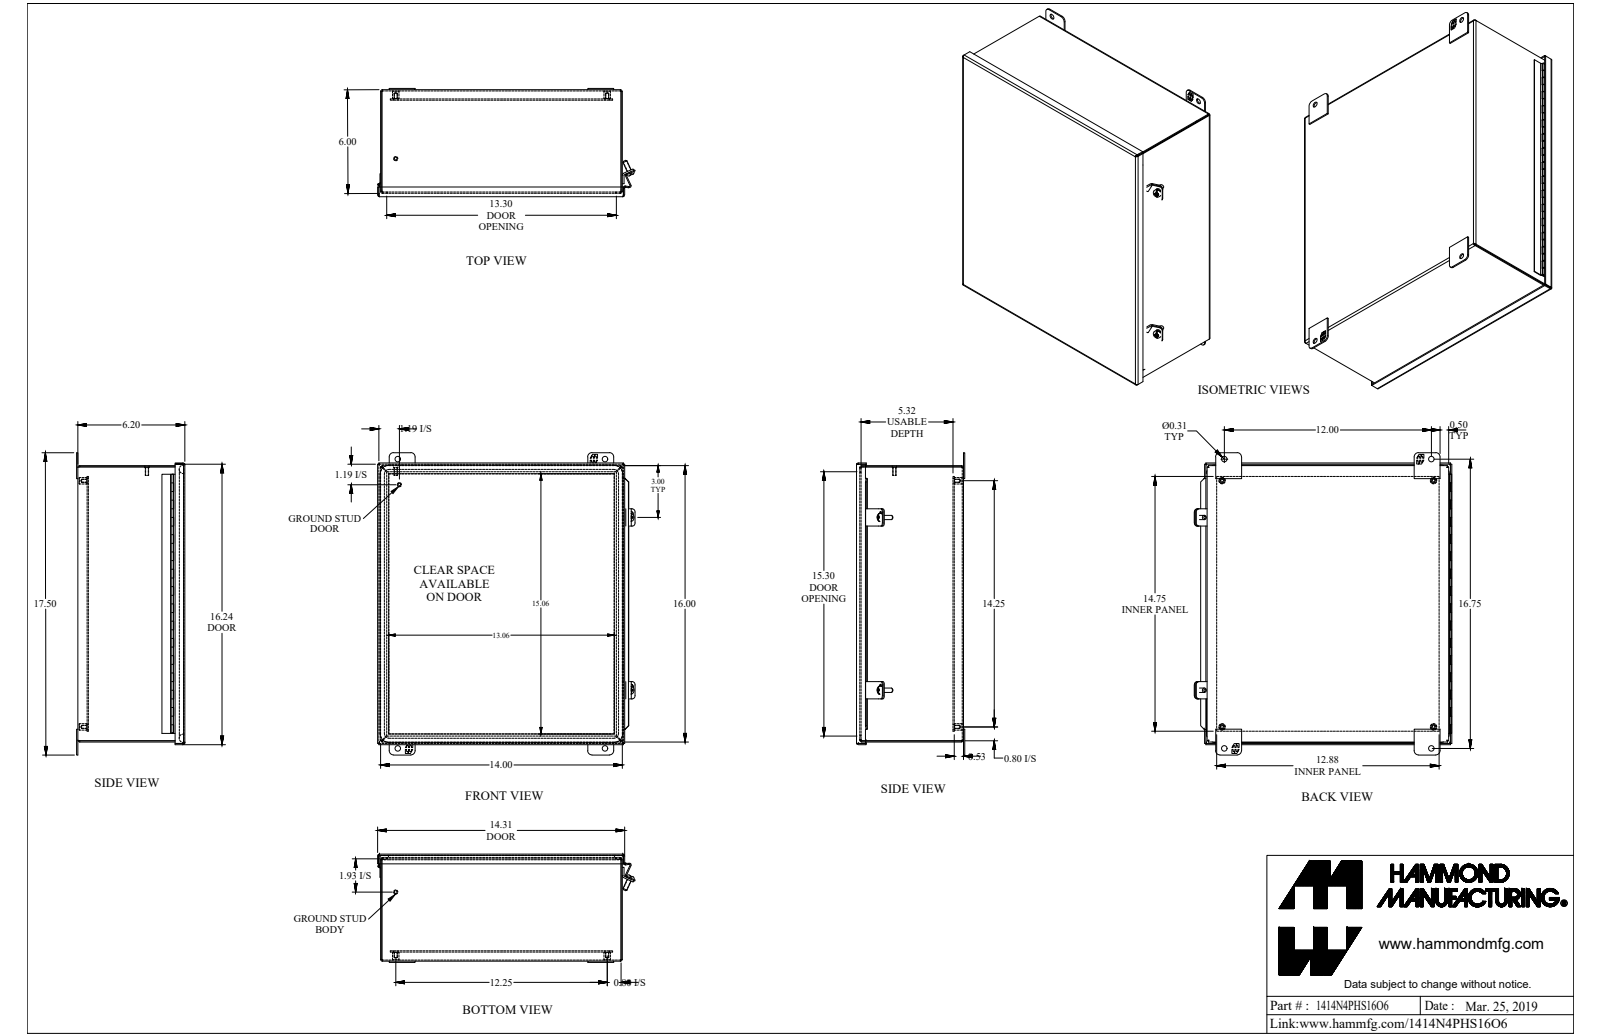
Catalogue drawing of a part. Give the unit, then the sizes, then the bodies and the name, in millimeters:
Units: millimetres
Overall size (bounding box): 444.5 × 378.5 × 159.2
Round holes (diameter × count): ⌀4 ×4, ⌀6.7 ×4, ⌀8 ×4, ⌀5.4 ×2, ⌀1.3 ×1
Round bosses / shafts (diameter × count): ⌀9.5 ×4, ⌀6.4 ×4, ⌀12.2 ×2, ⌀4.8 ×2, ⌀2.5 ×1, ⌀1.1 ×1
Partial cylindrical surfaces — rounded edges, fillets, slot ends (radius × count): R6.4 ×24, R0.9 ×9, R2.7 ×9, R4.8 ×8, R0.2 ×4, R1.2 ×4, R2 ×4, R3 ×4
Main face-to-face distances: 1.8, 155.6, 142.1, 13.5, 157.4, 153.7, 15.3, 143.9, 11.7, 140.2
Hole centre spacings: 309.6, 311.2, 499.8, 31.9, 393.7, 31.9, 304.8, 362
Volume: 1 357 000 mm³ · Surface area: 1 496 000 mm²
Bodies: 21 solids, 778 faces (496 planar, 220 cylindrical, 62 other)
Part name (STEP PRODUCT): 1414N4PHS16O6
STEP written by: SolidWorks 2018 (AUTOMOTIVE_DESIGN)
